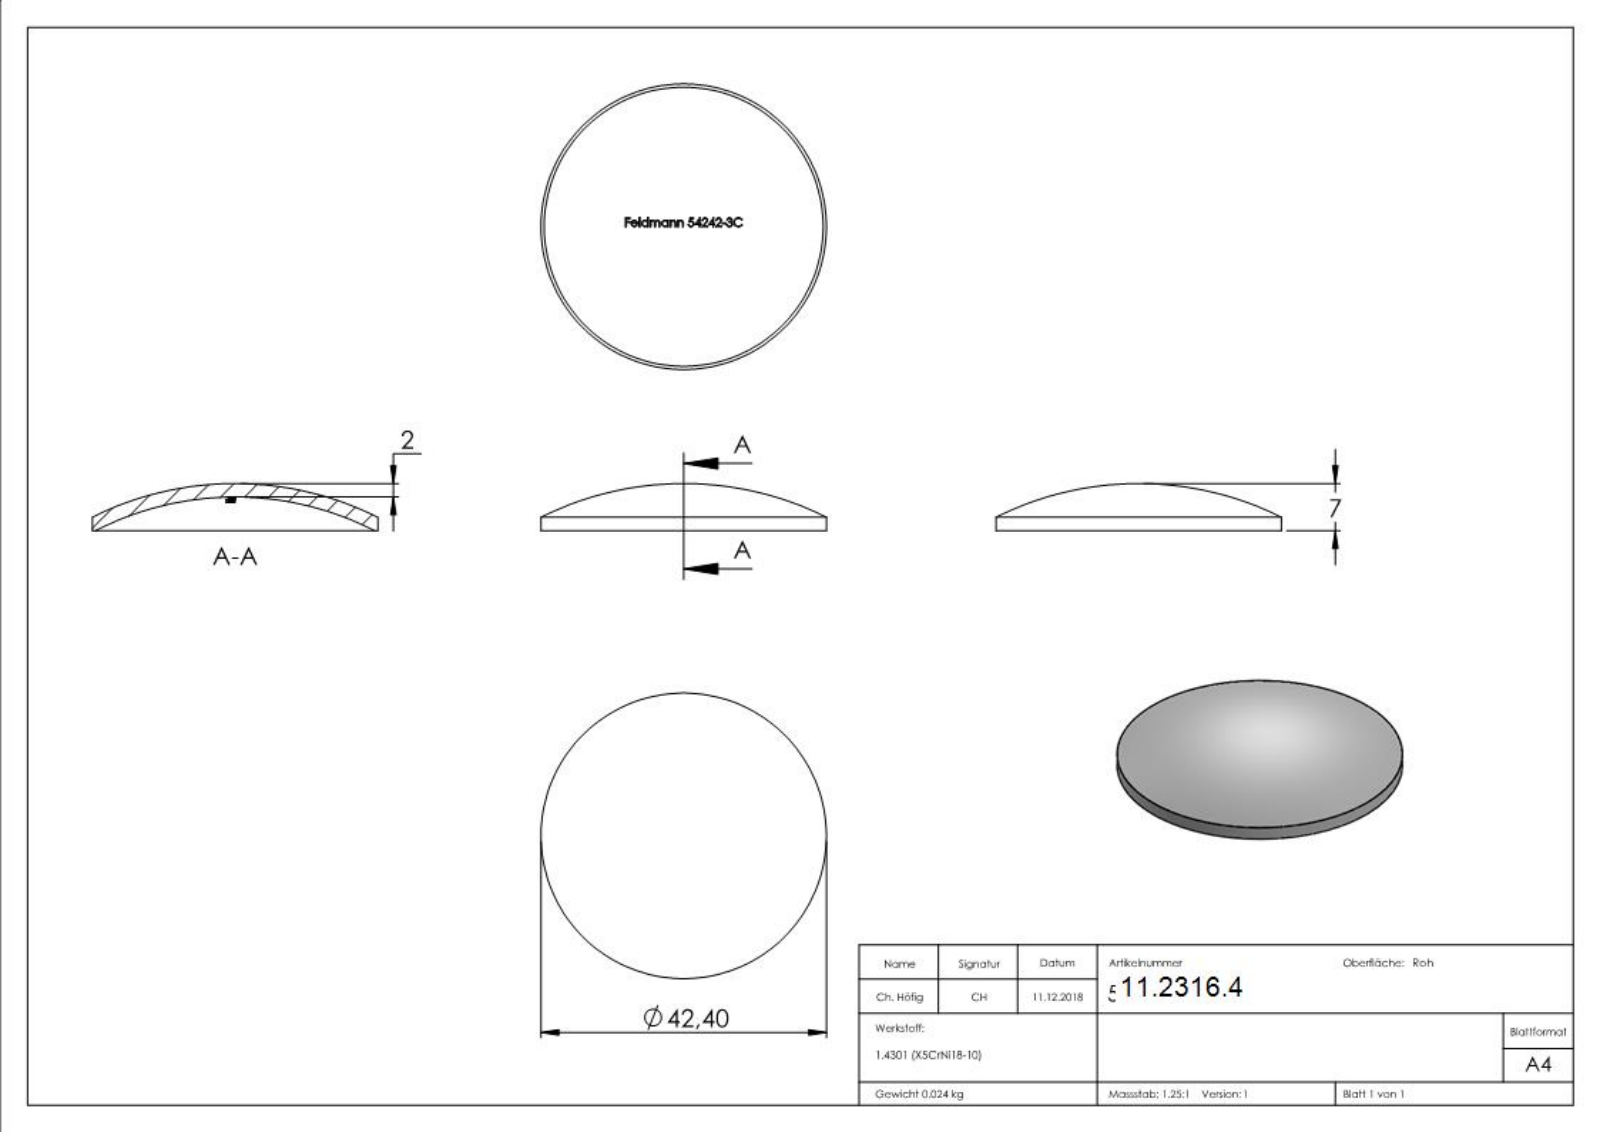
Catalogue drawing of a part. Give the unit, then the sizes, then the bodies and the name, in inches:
Units: inches
Overall size (bounding box): 1.669 × 1.669 × 0.276
Round bosses / shafts (diameter × count): ⌀1.669 ×1
Main face-to-face distances: 0.017, 0.117, 0.015, 0.08, 0.054, 0.035, 0.049, 0.431, 0.351, 0.08
Volume: 0.182 in³ · Surface area: 5.048 in²
Bodies: 1 solid, 238 faces (108 planar, 2 cylindrical, 128 other)
Part name (STEP PRODUCT): 54242-3C
STEP written by: SolidWorks 2015 (CONFIG_CONTROL_DESIGN)
